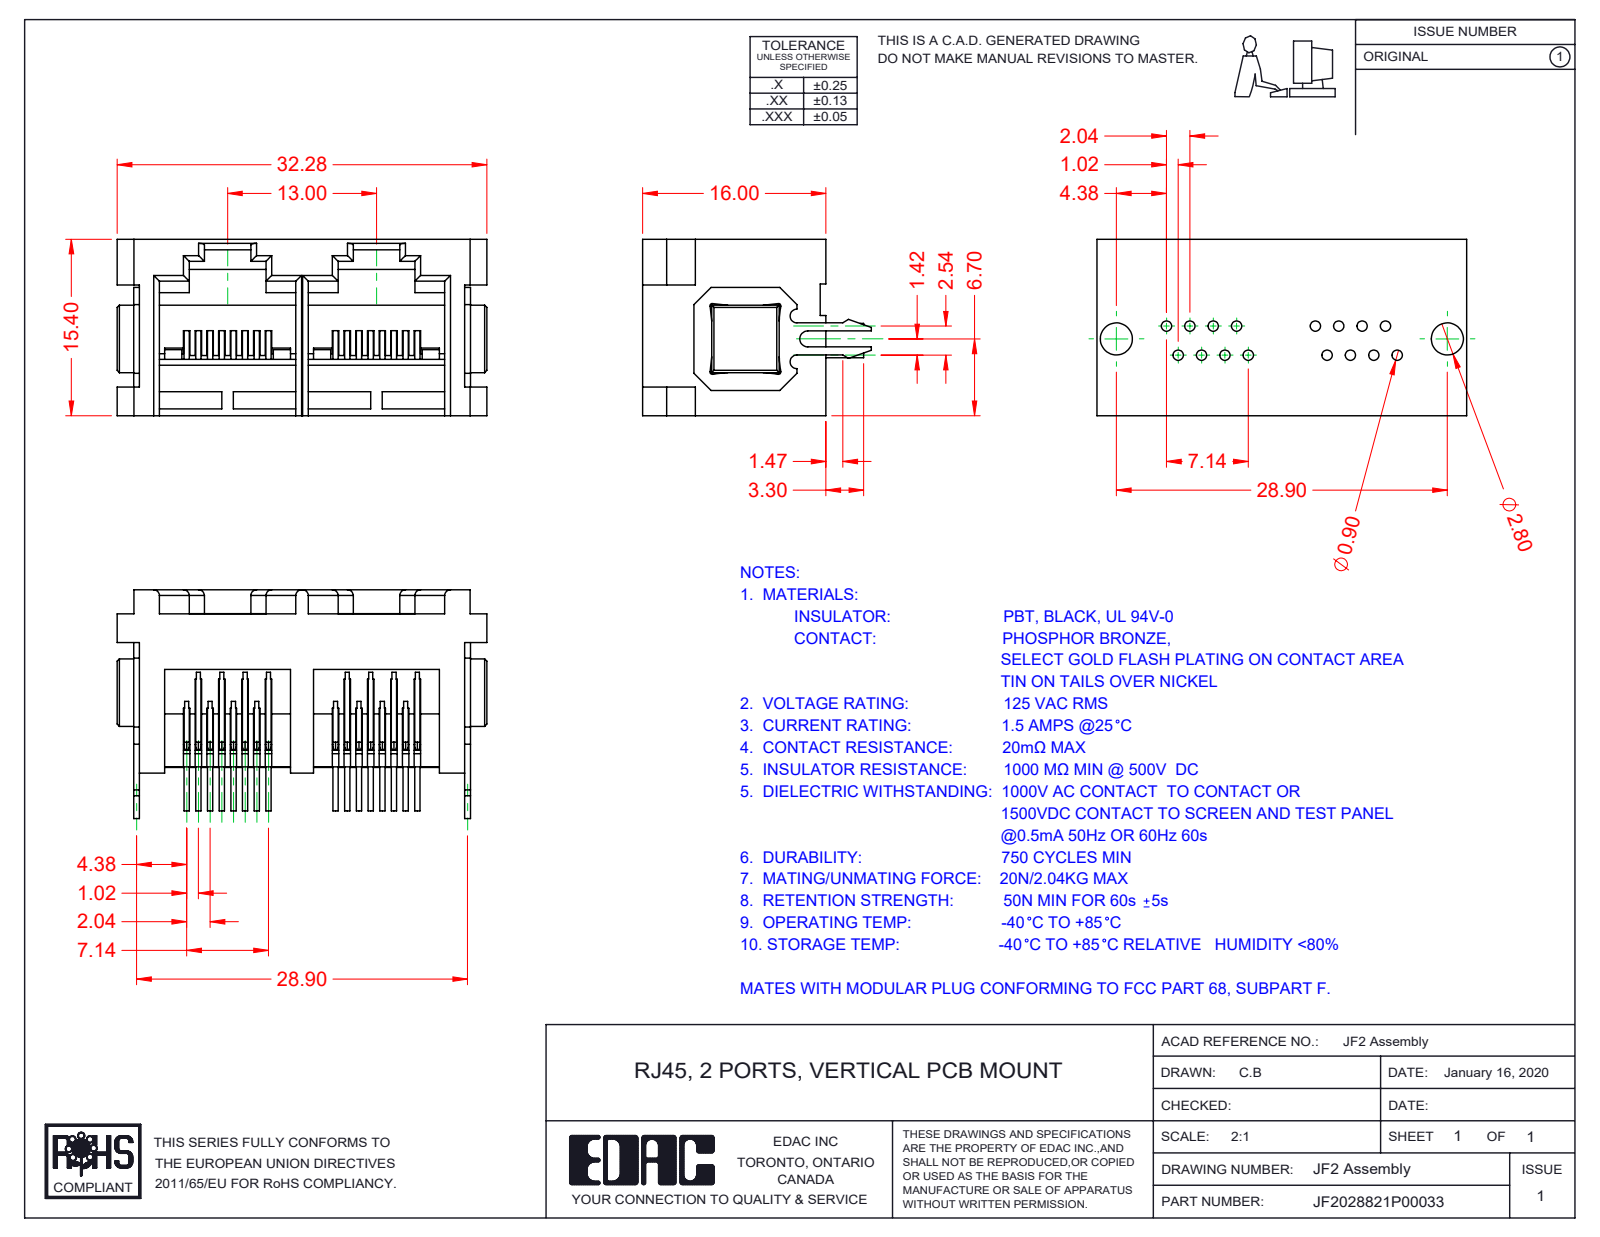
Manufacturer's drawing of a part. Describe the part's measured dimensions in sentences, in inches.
The part is named "F2 Insulator; RJF2028821P00033; F2 Contact Lock; F2 Contacts (+1 more)". Its 3-D file was written by "SolidWorks 2016 (CONFIG_CONTROL_DESIGN)". It is 21 solids with 1130 faces: 734 planar, 300 cylindrical and 96 other. Overall it measures 1.271 by 0.786 by 0.606 inches. Its volume is 0.215 cubic inches and its surface area 10.71 square inches. Round bosses or shafts: 64 of diameter 0.018. Partial cylindrical surfaces (rounded edges, fillets, slot ends): 32 of radius 0.007, 15 of radius 0.02, 4 of radius 0.008, 4 of radius 0.801, 3 of radius 0.012, 2 of radius 0.024, 1 of radius 0.008, 1 of radius 0.018. The main face-to-face distances are 0.496, 0.083, 0.512, 0.059, 0.111, 0.036, 0.459, 0.02, 1.118, 0.433.
